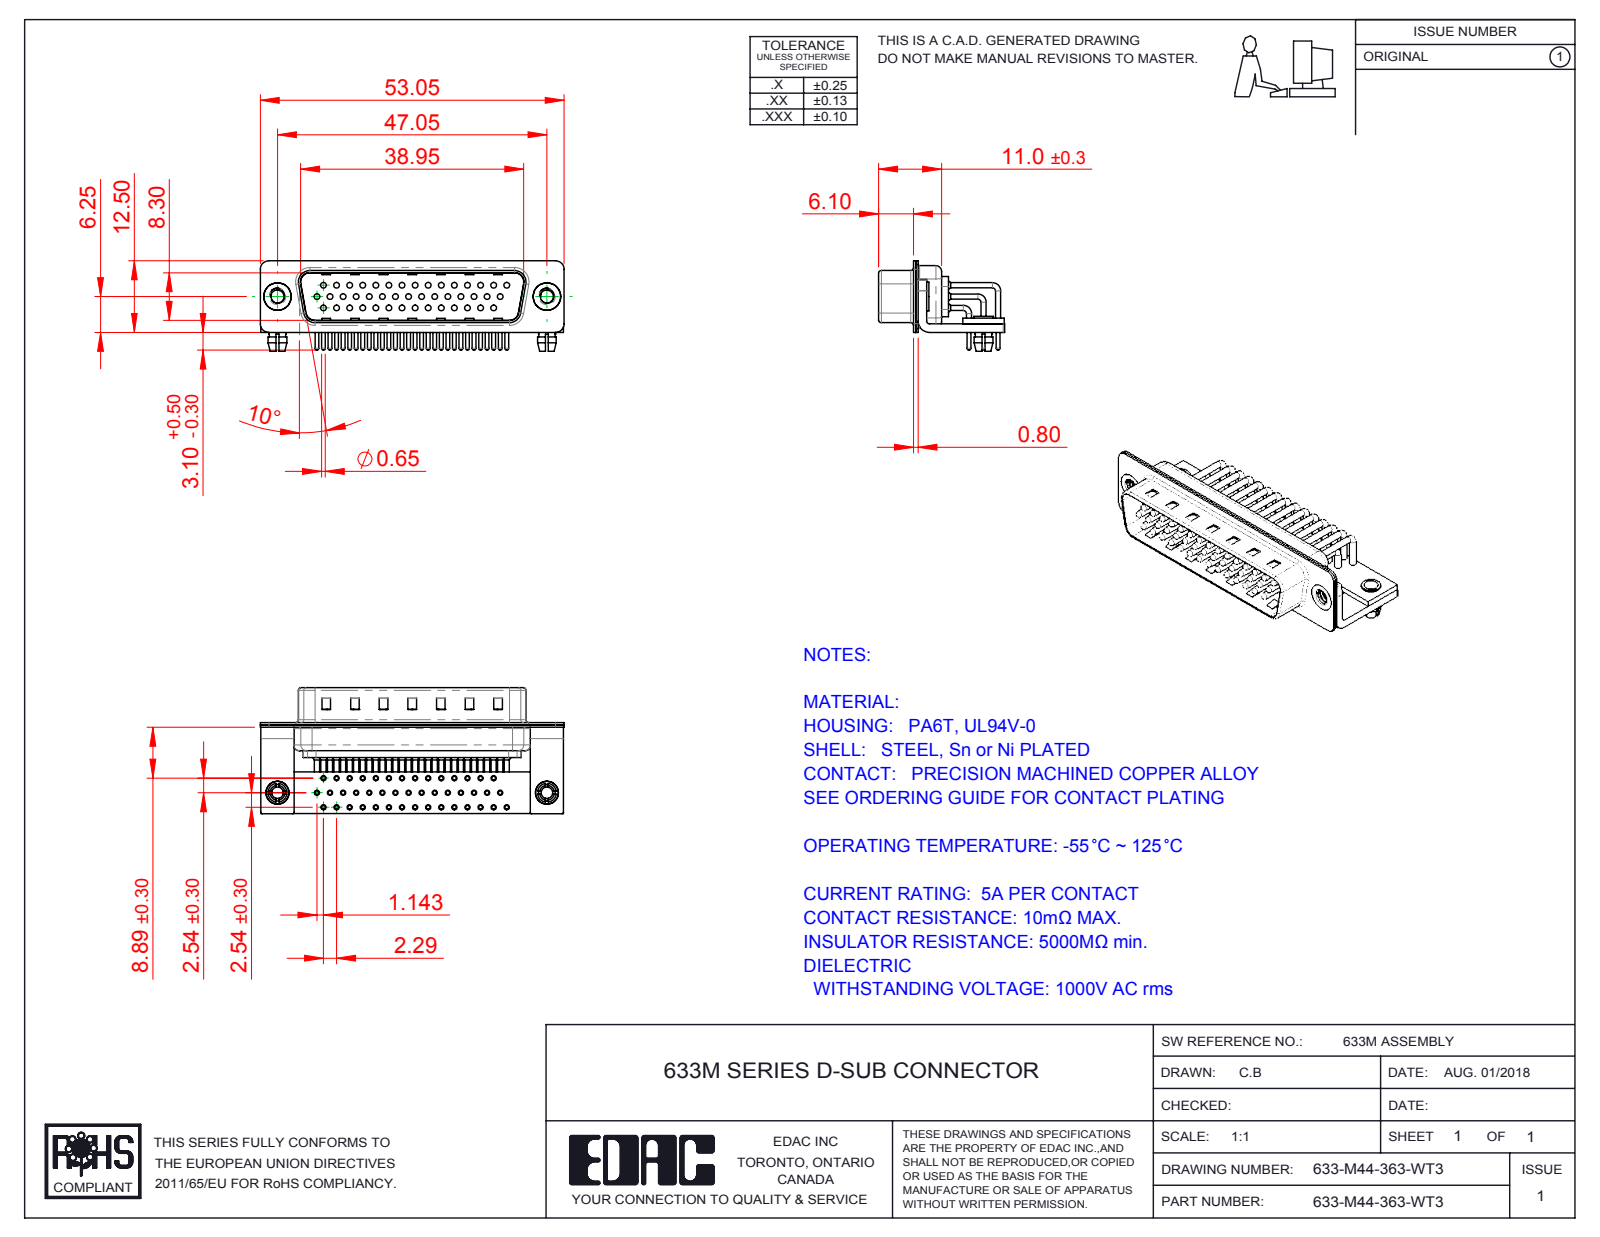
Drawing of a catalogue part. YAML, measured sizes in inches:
part_name: "633M Contact Row 1; 633M 4-40 Threaded Rivet_Stabilizer; 633M Contact Row 3; 633M Shell Front_44 Contacts (+7 more)"
step_written_by: "SolidWorks 2016 (CONFIG_CONTROL_DESIGN)"
units: inches
bodies: {solids: 54, faces: 5446, planar: 3061, cylindrical: 1863, other: 522}
overall_size: [2.089, 0.866, 0.622]
volume: 0.232
surface_area: 18.37
round_holes:
  - {diameter: 0.079, count: 46}
  - {diameter: 0.035, count: 44}
  - {diameter: 0.039, count: 44}
  - {diameter: 0.067, count: 44}
  - {diameter: 0.089, count: 2}
  - {diameter: 0.098, count: 2}
  - {diameter: 0.126, count: 2}
  - {diameter: 0.157, count: 2}
  - {diameter: 0.189, count: 2}
round_bosses_or_shafts:
  - {diameter: 0.035, count: 45}
  - {diameter: 0.059, count: 44}
  - {diameter: 0.026, count: 44}
  - {diameter: 0.197, count: 2}
  - {diameter: 0.193, count: 2}
  - {diameter: 0.157, count: 2}
  - {diameter: 0.134, count: 2}
  - {diameter: 0.13, count: 2}
partial_cylinders:
  - {radius: 0.04, count: 44}
  - {radius: 0.01, count: 16}
  - {radius: 0.059, count: 16}
  - {radius: 0.079, count: 13}
  - {radius: 0.02, count: 9}
  - {radius: 0.063, count: 8}
  - {radius: 0.024, count: 4}
  - {radius: 0.026, count: 4}
face_to_face_distances: [0.016, 0.059, 0.033, 0.049, 0.039, 0.075, 0.409, 0.031, 0.376, 0.327]
hole_center_spacings: [0.09, 0.09, 0.18, 0.27, 0.156, 0.45, 0.324, 0.63]
